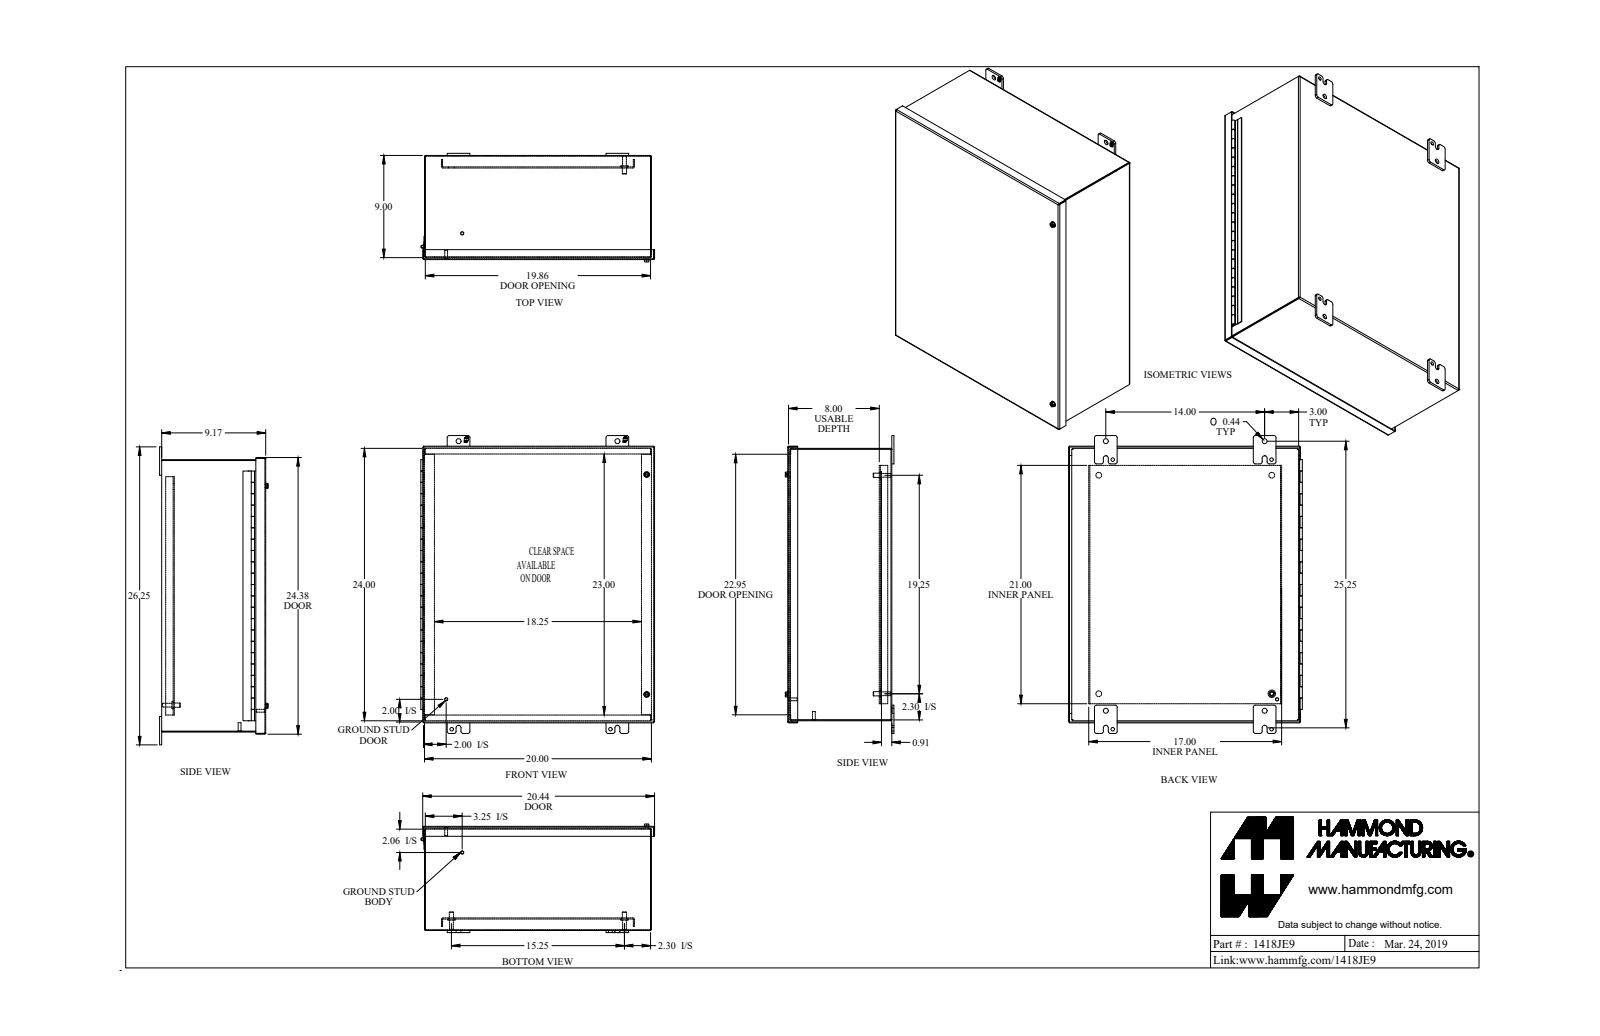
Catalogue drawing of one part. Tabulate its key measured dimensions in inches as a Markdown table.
| quantity | value |
| --- | --- |
| part name | 1418JE9_Default |
| STEP written by | SolidWorks 2018 (CONFIG_CONTROL_DESIGN) |
| units | inches |
| bodies | 32 solids, 942 faces (587 planar, 313 cylindrical, 42 other) |
| overall size | 26.25 × 20.604 × 9.571 |
| volume | 202.6 in³ |
| surface area | 5 019 in² |
| round holes (diameter × count) | 0.313 × 6, 0.437 × 4, 0.5 × 4, 0.26 × 2, 0.266 × 2, 0.28 × 2, 0.29 × 2, 0.307 × 2, 0.397 × 2, 0.445 × 2, 0.187 × 1, 3.5 × 1 |
| round bosses / shafts (diameter × count) | 0.65 × 4, 0.375 × 4, 0.33 × 4, 1 × 2, 0.51 × 2, 0.5 × 2, 0.39 × 2, 0.281 × 2 |
| partial cylindrical surfaces (radius × count) | 0.188 × 24, 0.25 × 20, 0.036 × 12, 0.108 × 12, 0.218 × 8, 0.133 × 6, 0.06 × 5, 0.125 × 4 |
| main face-to-face distances | 0.072, 9.1, 9.172, 9.028, 19.928, 0.095, 7.996, 8.091, 1.104, 1.032 |
| hole center spacings | 14, 12.279, 19.25, 20.759, 24.559, 0.059, 1.735, 1.736 |
